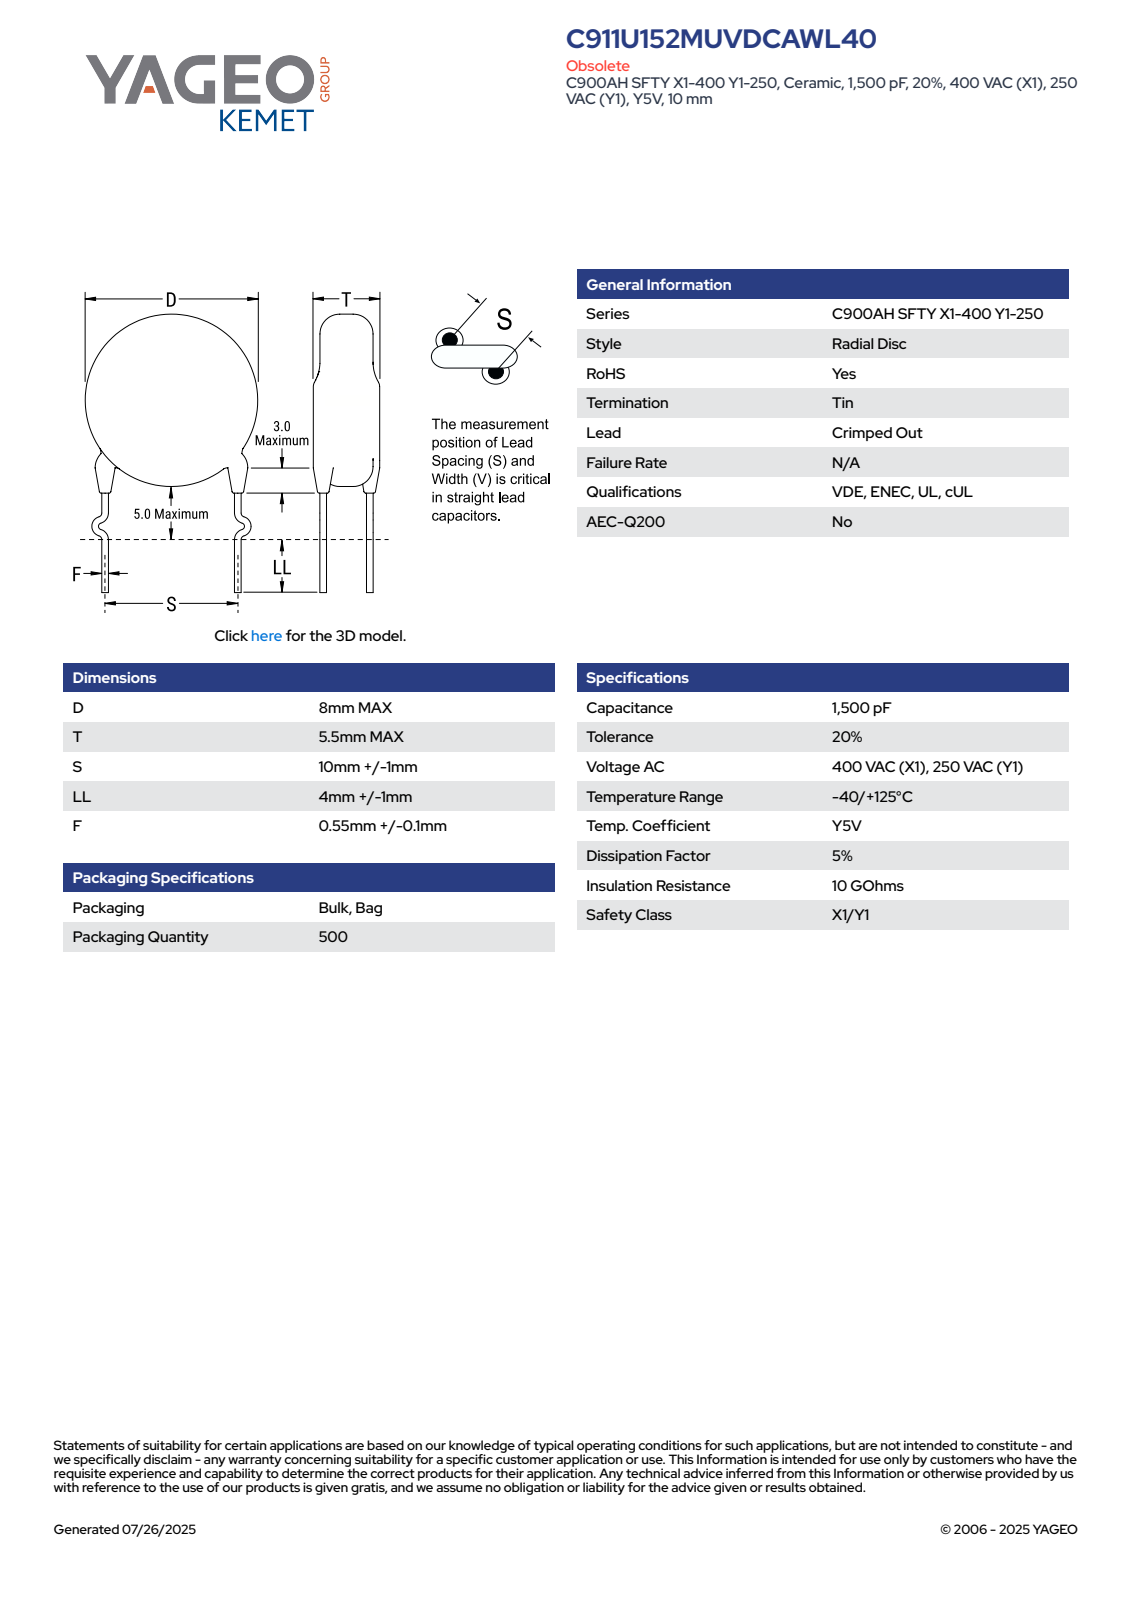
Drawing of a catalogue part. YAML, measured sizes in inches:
part_name: "CCD_KCOC900_D8T5.5S10LL5F0.55"
step_written_by: "SolidWorks 2014 (AUTOMOTIVE_DESIGN)"
units: inches
bodies: {solids: 4, faces: 93, planar: 63, cylindrical: 10, other: 20}
overall_size: [0.709, 0.55, 0.265]
volume: 0.017
surface_area: 0.457
round_bosses_or_shafts:
  - {diameter: 0.047, count: 4}
  - {diameter: 0.315, count: 1}
face_to_face_distances: [0.217, 0.033, 0.174, 0.141, 0.133, 0.02, 0.012, 0.026, 0.067, 0.097]
